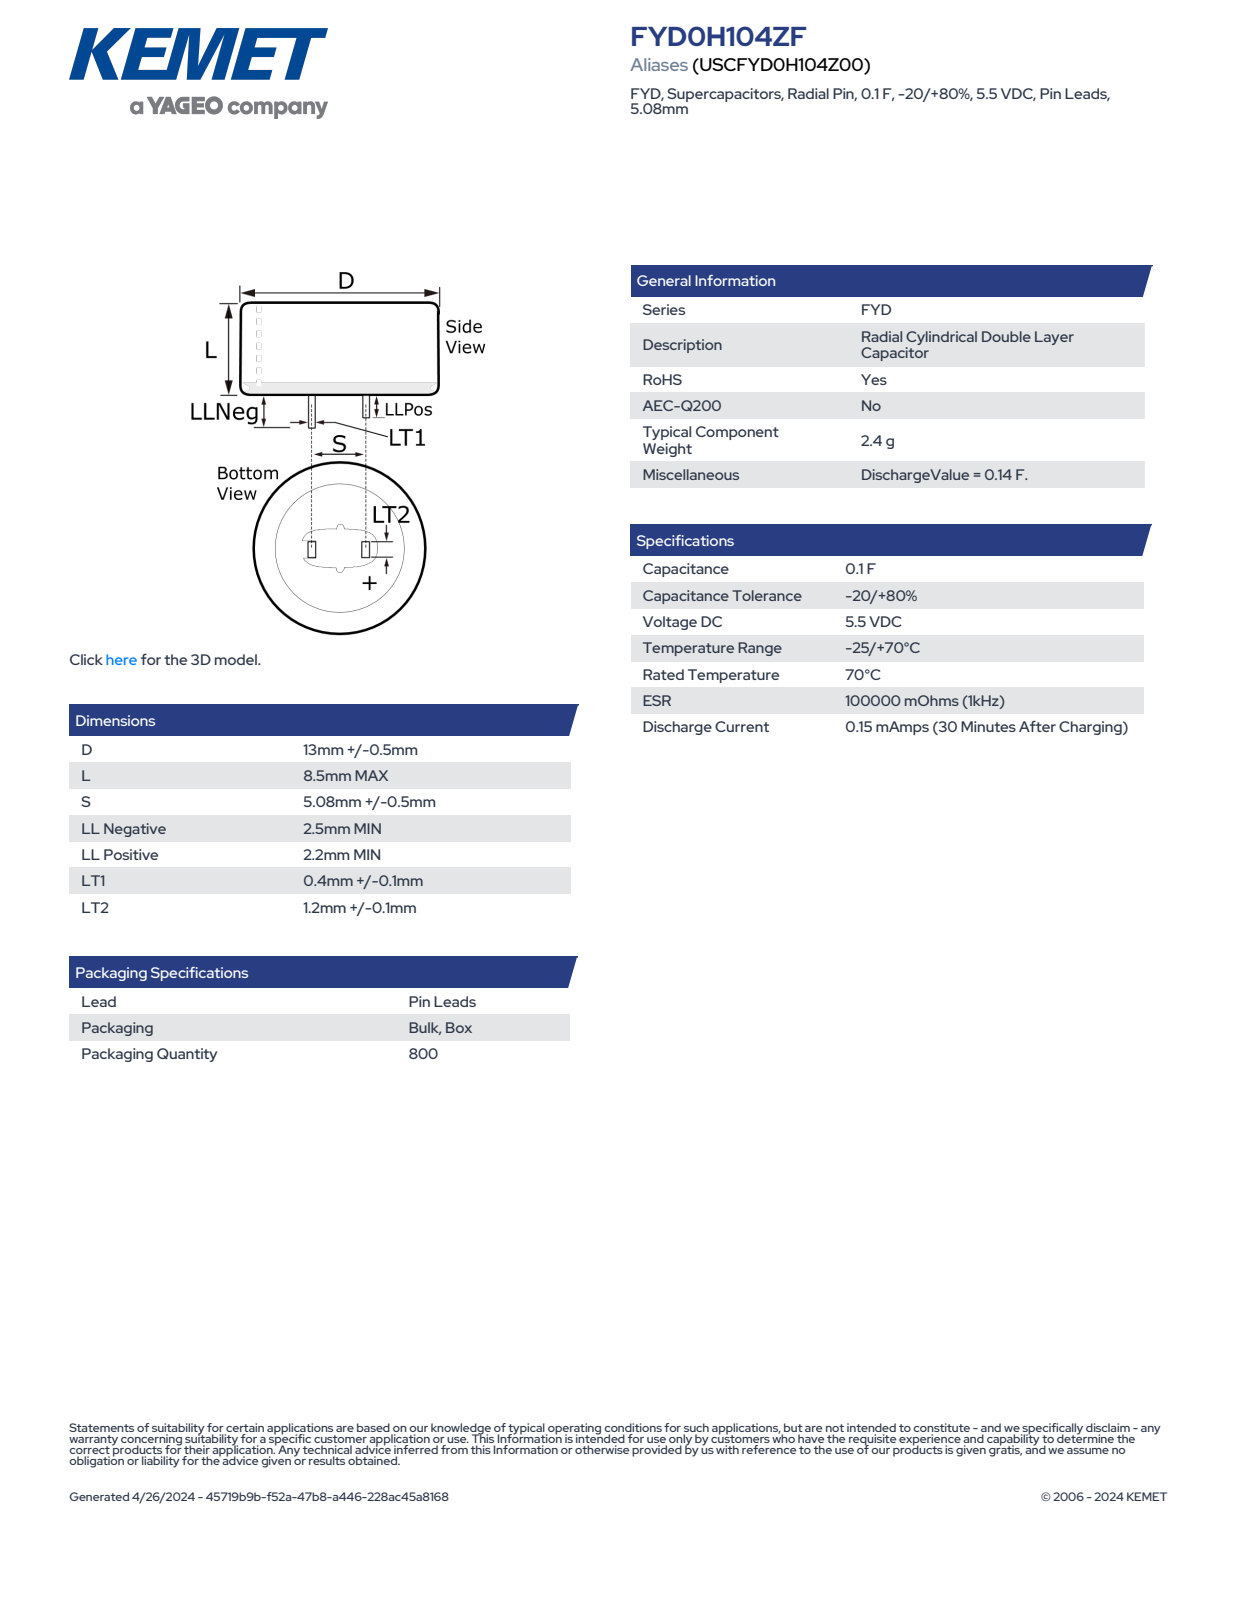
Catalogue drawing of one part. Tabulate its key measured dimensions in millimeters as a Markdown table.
| quantity | value |
| --- | --- |
| part name | CDR_LPLLN_D13.5L8.5S5.08LLNEG2.5LLPOS2.2LT10.5LT21.3 |
| STEP written by | SolidWorks 2014 (AUTOMOTIVE_DESIGN) |
| units | millimeters |
| bodies | 1 solid, 78 faces (70 planar, 4 cylindrical, 4 other) |
| overall size | 13.5 × 13.5 × 11 |
| volume | 1 214 mm³ |
| surface area | 644 mm² |
| round bosses / shafts (diameter × count) | 13.5 × 1 |
| partial cylindrical surfaces (radius × count) | 6.76 × 1 |
| main face-to-face distances | 8.5, 0.5, 5.08, 5.58, 4.58, 1.3, 2.2, 10.7, 2.5, 11 |
